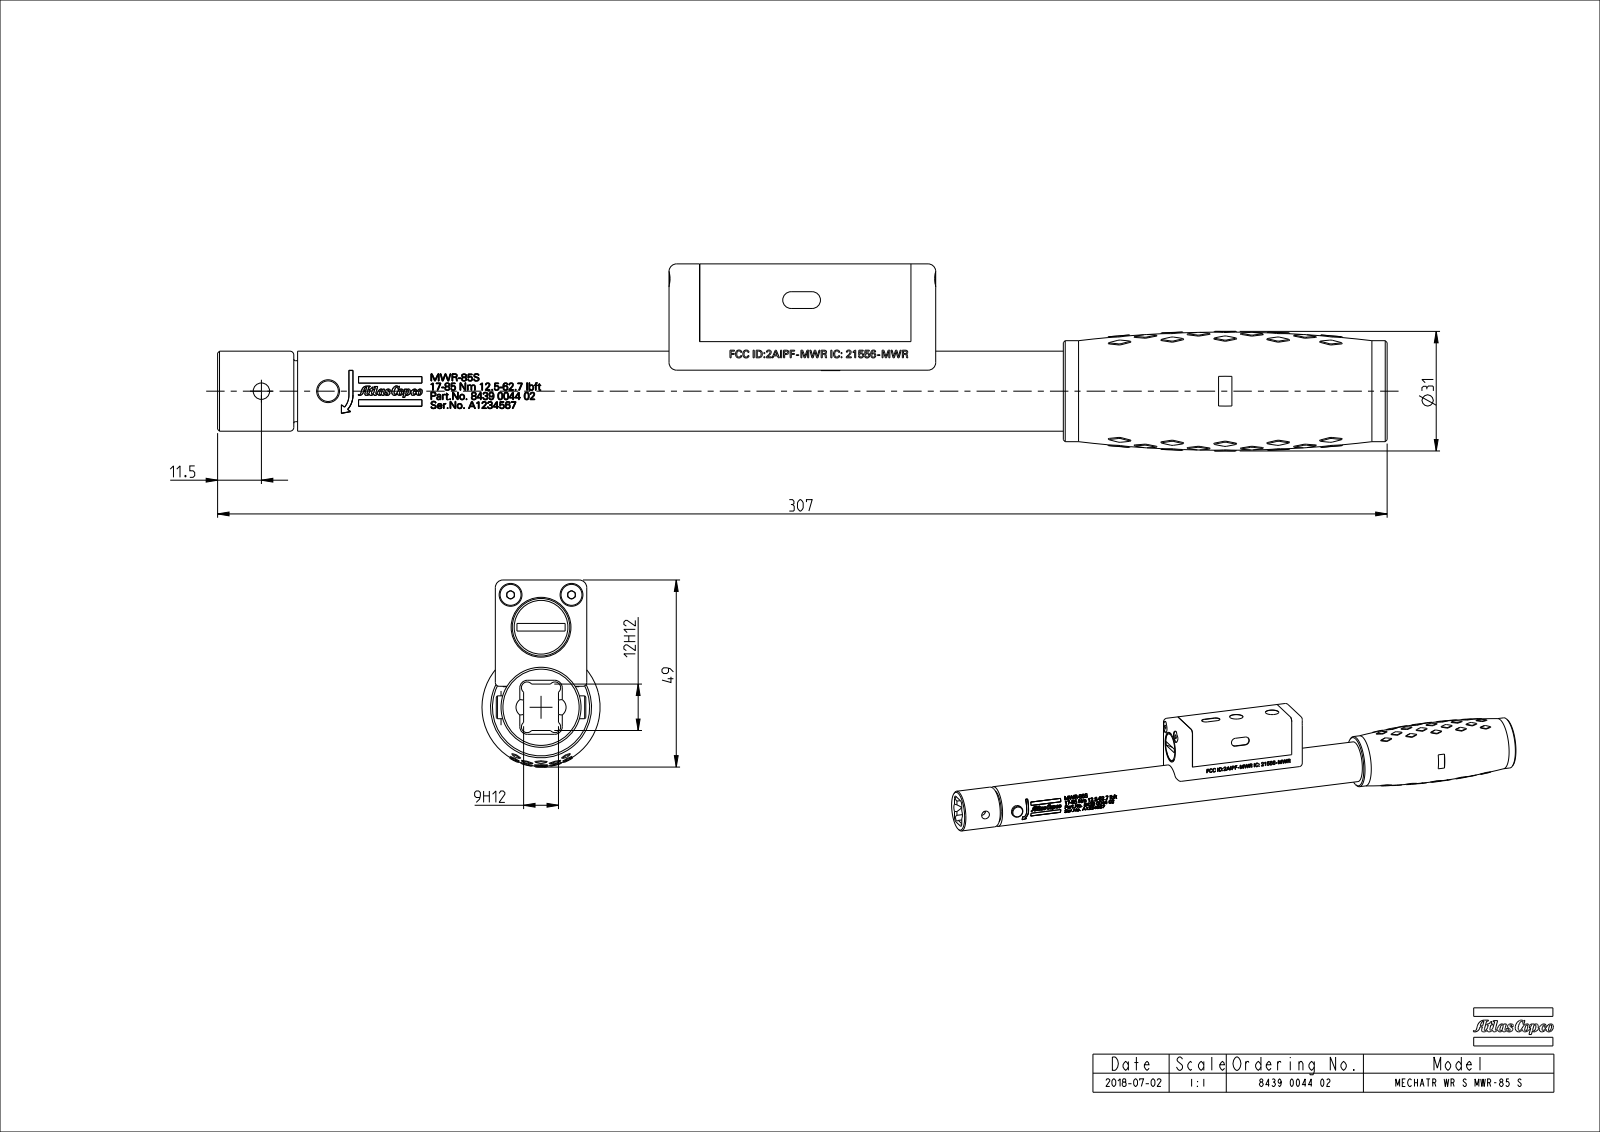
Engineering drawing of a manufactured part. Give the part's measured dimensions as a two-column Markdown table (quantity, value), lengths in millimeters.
| quantity | value |
| --- | --- |
| part name | 8439004402_SW |
| STEP written by | CREO PARAMETRIC BY PTC INC, 2016260 (CONFIG_CONTROL_DESIGN) |
| units | millimeters |
| bodies | 0 solids, 215 faces (23 planar, 118 cylindrical, 74 other) |
| overall size | 307 × 49.11 × 31 |
| round bosses / shafts (diameter × count) | 26.5 × 1, 21 × 1, 16 × 1, 6 × 1 |
| partial cylindrical surfaces (radius × count) | 2 × 8, 1 × 2, 10.4 × 1 |
| main face-to-face distances | 24, 118.5, 188.5, 85, 33.5, 103.5, 70, 307, 222, 120.6 |
